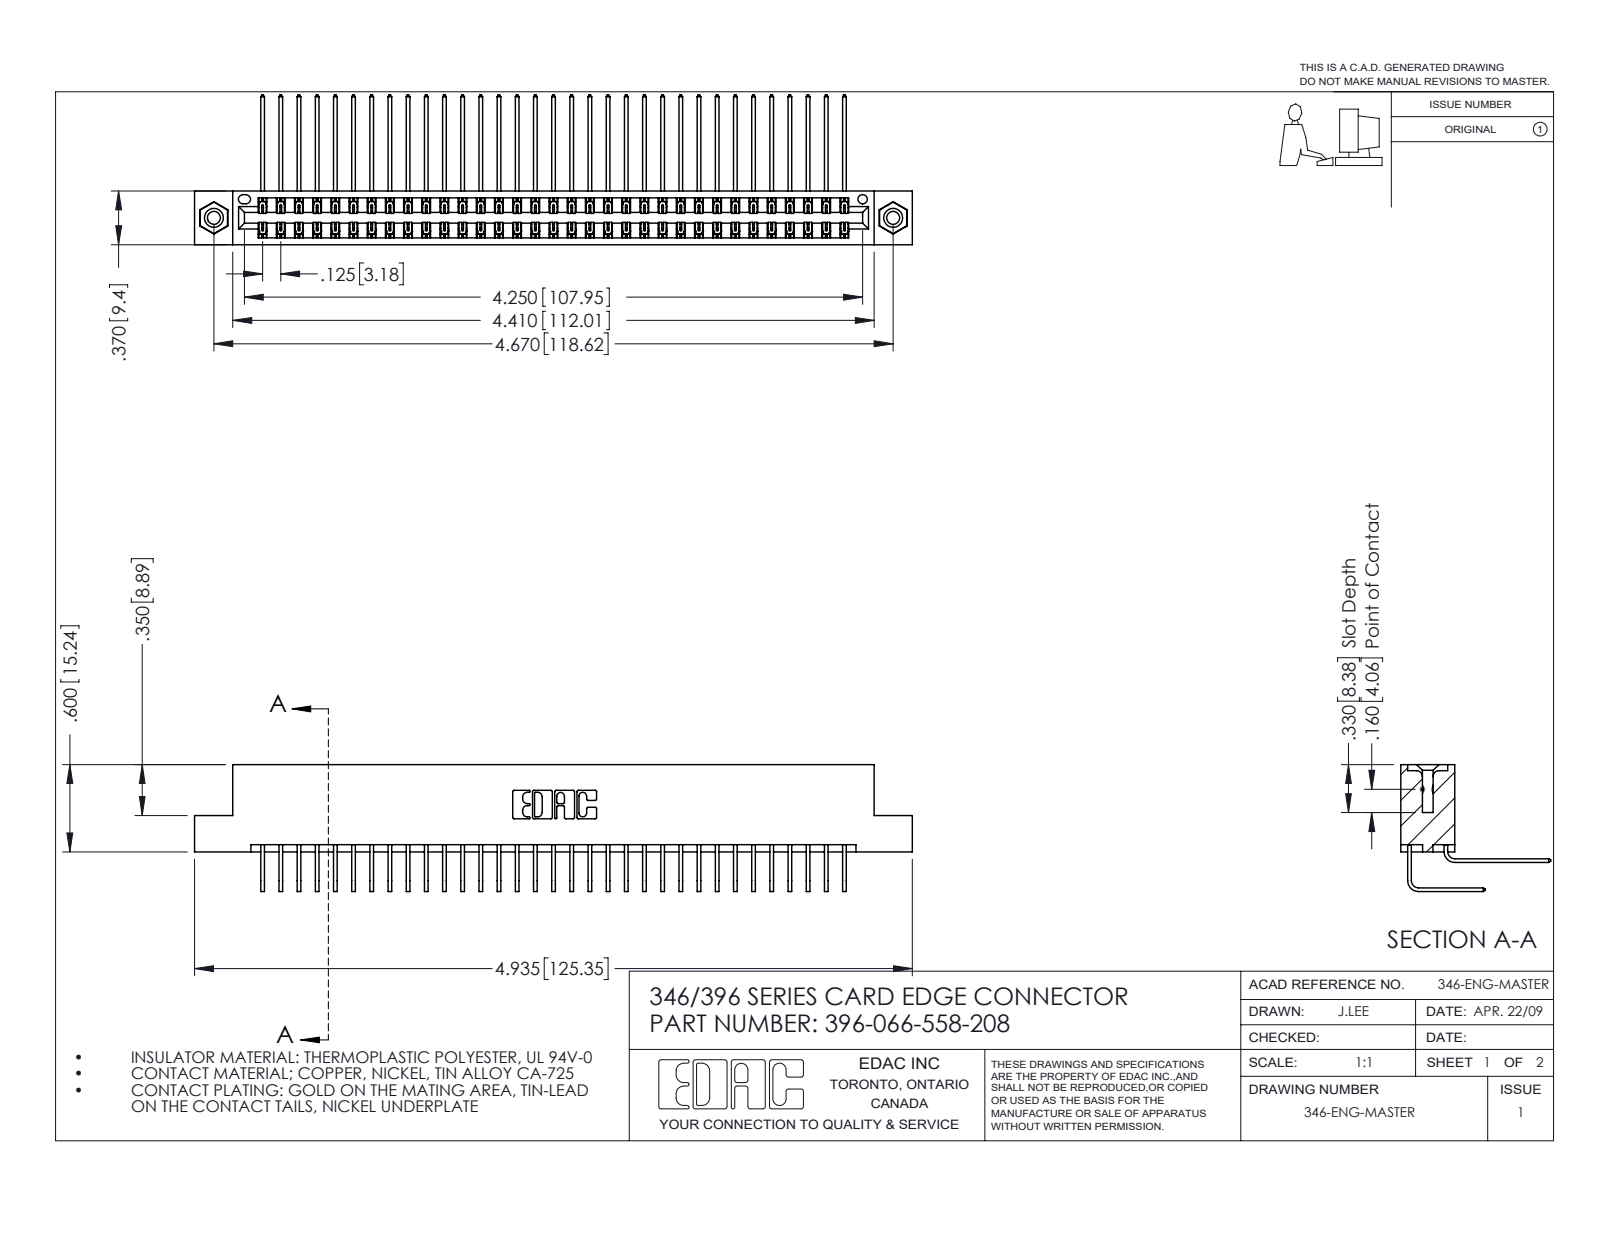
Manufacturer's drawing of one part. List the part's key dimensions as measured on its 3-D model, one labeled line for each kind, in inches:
Part name (STEP PRODUCT): 345-250-001_345-250-003-102; 345-292-001_558 559 Tail - 1; 346 Part_Flush Mounting Lugs - 0.156 Dia-TI; 345-292-001_558 Tail - 2 (+1 more)
STEP written by: SolidWorks 2016 (CONFIG_CONTROL_DESIGN)
Units: inches
Bodies: 69 solids, 3746 faces (2550 planar, 1180 cylindrical, 16 other)
Overall size (bounding box): 4.935 × 1.03 × 0.873
Volume: 0.764 in³ · Surface area: 29.33 in²
Round holes (diameter × count): ⌀0.089 ×2, ⌀0.125 ×2, ⌀0.156 ×2, ⌀0.064 ×1
Round bosses / shafts (diameter × count): ⌀0.155 ×2
Partial cylindrical surfaces — rounded edges, fillets, slot ends (radius × count): R0.006 ×99, R0.01 ×22, R0.007 ×6, R0.031 ×6, R0.026 ×3, R0.014 ×2, R0.022 ×2, R0.024 ×2
Main face-to-face distances: 0.048, 0.322, 0.025, 0.37, 0.25, 0.072, 0.298, 0.275, 0.148, 0.222
Hole centre spacings: 0.246, 4.462, 4.67
